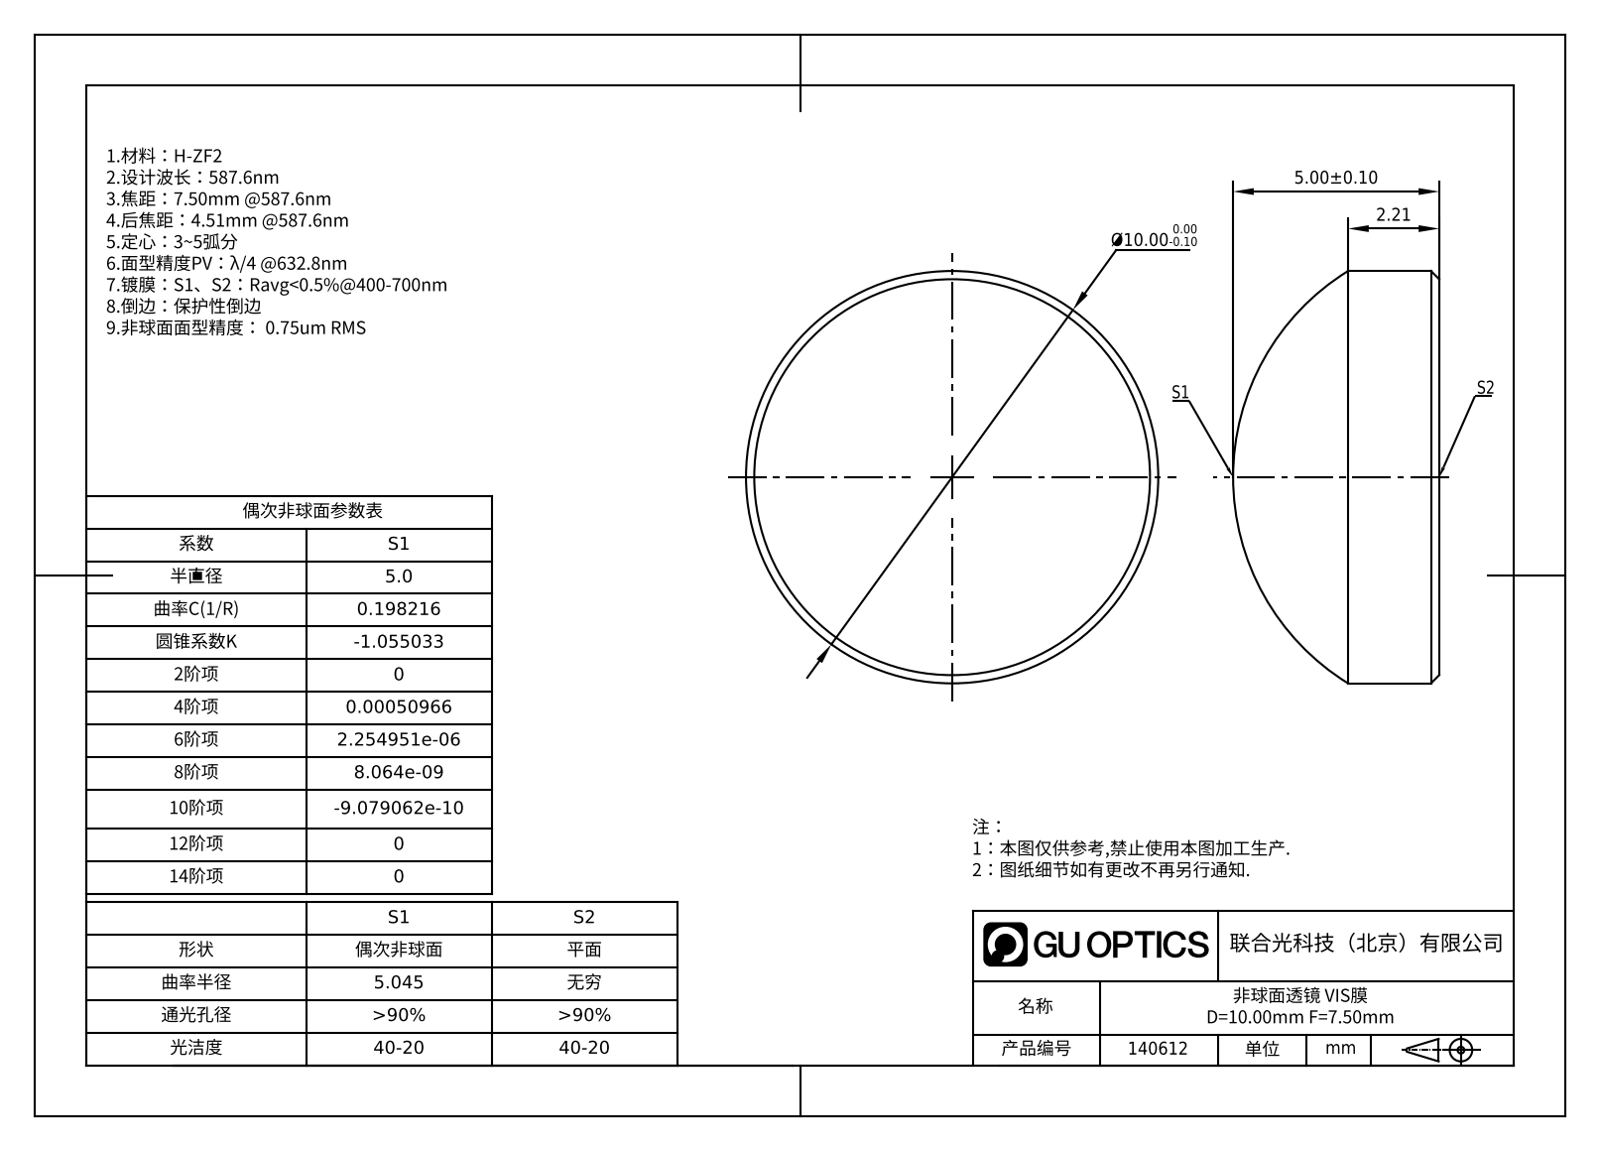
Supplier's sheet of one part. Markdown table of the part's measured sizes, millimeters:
| quantity | value |
| --- | --- |
| part name | GLA11-010-7.5-VIS |
| STEP written by | SolidWorks 2022 (AUTOMOTIVE_DESIGN) |
| units | millimeters |
| bodies | 1 solid, 7 faces (1 planar, 2 cylindrical, 4 other) |
| overall size | 10 × 10 × 5 |
| volume | 294 mm³ |
| surface area | 247 mm² |
| round bosses / shafts (diameter × count) | 10 × 1 |
